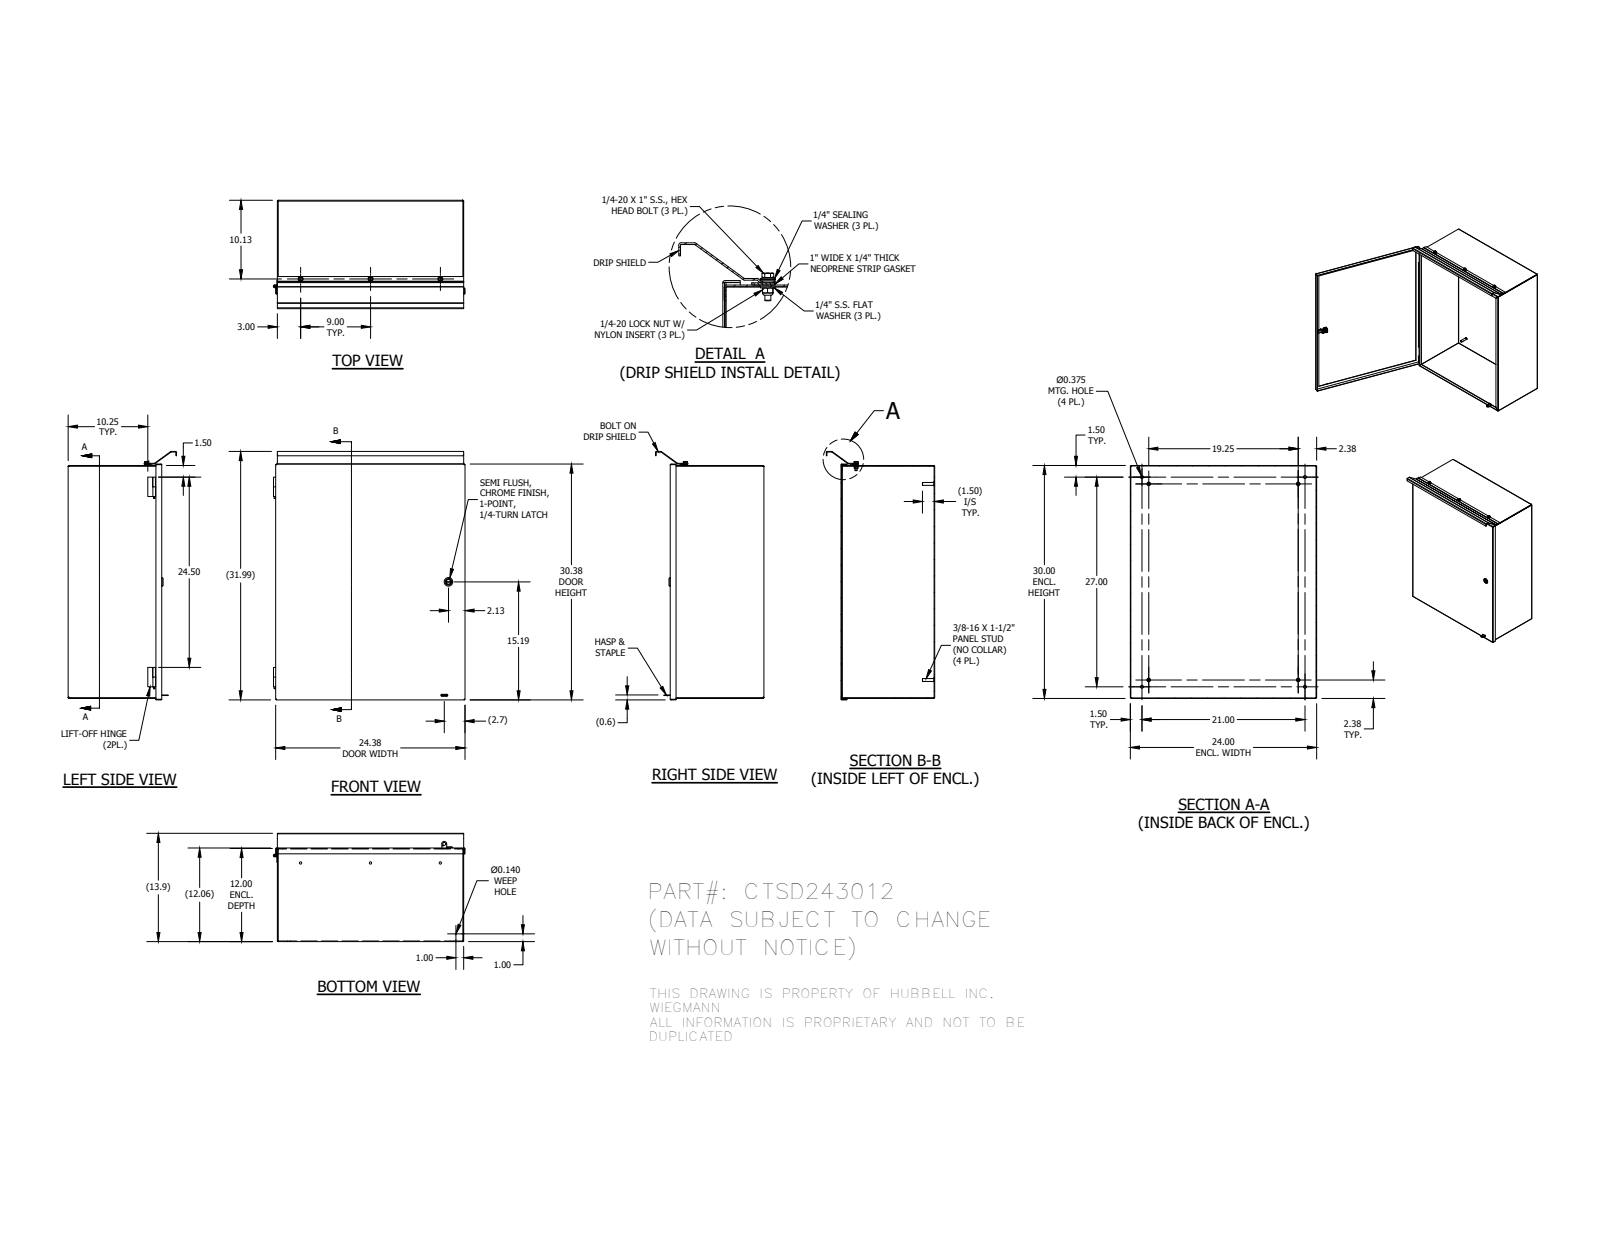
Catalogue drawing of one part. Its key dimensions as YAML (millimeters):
part_name: "CTSD243012BKP; CTSD2430DR; 31815; HC2527 (+8 more)"
step_written_by: "Autodesk Inventor 2014 (AUTOMOTIVE_DESIGN)"
units: millimeters
bodies: {solids: 36, faces: 860, planar: 456, cylindrical: 259, other: 145}
overall_size: [812.67, 626.48, 354.32]
volume: 3774000
surface_area: 4044000
round_holes:
  - {diameter: 9.52, count: 5}
  - {diameter: 4.98, count: 3}
  - {diameter: 5.97, count: 3}
  - {diameter: 6.99, count: 3}
  - {diameter: 7.14, count: 3}
  - {diameter: 7.37, count: 3}
  - {diameter: 3.17, count: 1}
  - {diameter: 3.56, count: 1}
  - {diameter: 5, count: 1}
  - {diameter: 5.36, count: 1}
  - {diameter: 5.56, count: 1}
  - {diameter: 8, count: 1}
round_bosses_or_shafts:
  - {diameter: 11.73, count: 4}
  - {diameter: 9.52, count: 4}
  - {diameter: 16.51, count: 3}
  - {diameter: 15.88, count: 3}
  - {diameter: 15.24, count: 3}
  - {diameter: 11.13, count: 3}
  - {diameter: 11.05, count: 3}
  - {diameter: 6.6, count: 3}
partial_cylinders:
  - {radius: 0.3, count: 30}
  - {radius: 0.79, count: 20}
  - {radius: 2.67, count: 18}
  - {radius: 0.5, count: 10}
  - {radius: 1.78, count: 8}
  - {radius: 3.17, count: 4}
  - {radius: 4, count: 4}
  - {radius: 0.4, count: 3}
face_to_face_distances: [1.88, 304.4, 302.52, 306.28, 607.72, 760.12, 609.6, 605.84, 762, 758.24]
hole_center_spacings: [228.6, 343.1, 533.4, 624.3, 685.8, 868.81, 7.32, 57.12]
